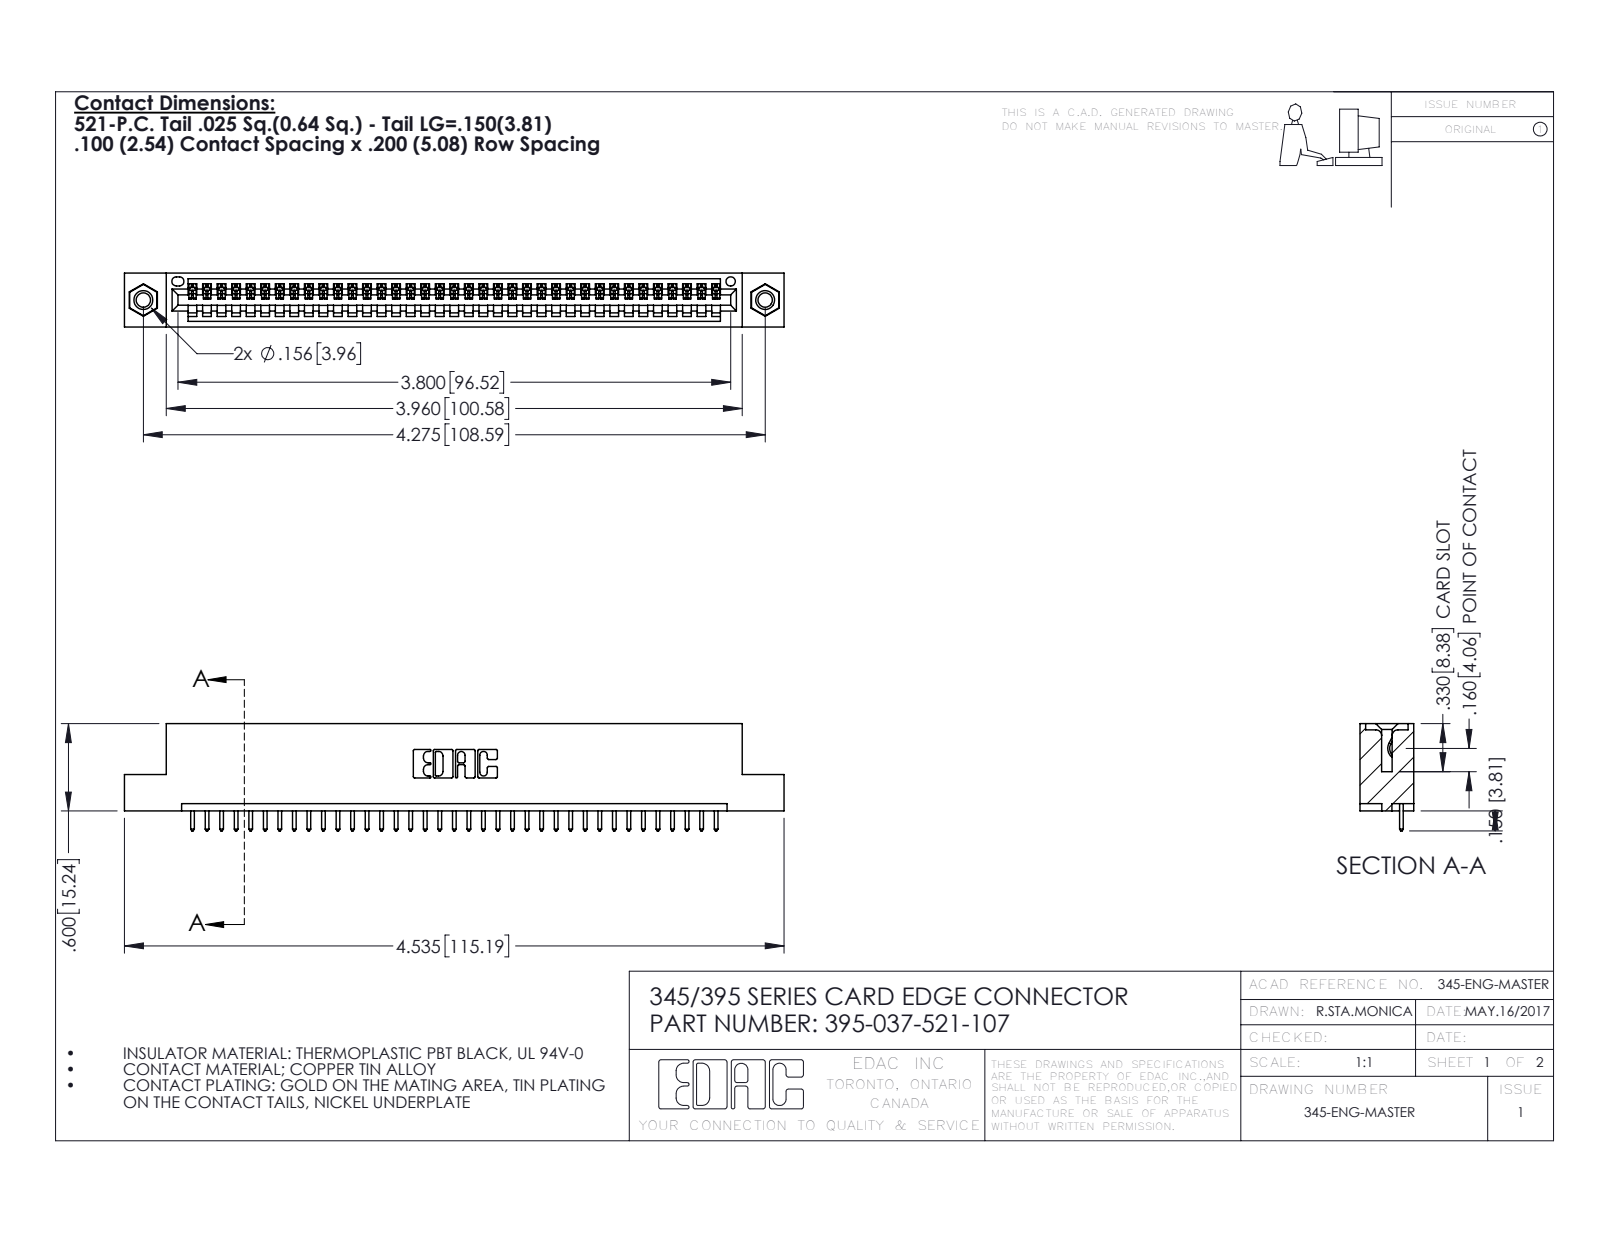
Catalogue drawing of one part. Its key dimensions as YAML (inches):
part_name: "345-250-001_345-250-005-103; 345-292-001_345-293-121; 345 Part_Flush Mounting Lugs - 0.156 Dia-TI; 395-037-521-107"
step_written_by: "SolidWorks 2016 (CONFIG_CONTROL_DESIGN)"
units: inches
bodies: {solids: 40, faces: 2332, planar: 1592, cylindrical: 724, other: 16}
overall_size: [4.535, 0.737, 0.37]
volume: 0.658
surface_area: 21.51
round_holes:
  - {diameter: 0.098, count: 2}
  - {diameter: 0.125, count: 2}
  - {diameter: 0.156, count: 2}
  - {diameter: 0.064, count: 1}
round_bosses_or_shafts:
  - {diameter: 0.155, count: 2}
partial_cylinders:
  - {radius: 0.006, count: 74}
  - {radius: 0.01, count: 74}
  - {radius: 0.01, count: 22}
  - {radius: 0.007, count: 6}
  - {radius: 0.031, count: 6}
  - {radius: 0.026, count: 3}
  - {radius: 0.031, count: 2}
  - {radius: 0.04, count: 2}
face_to_face_distances: [0.072, 0.298, 0.37, 0.2, 0.098, 0.272, 0.025, 0.225, 0.149, 0.072]
hole_center_spacings: [0.27, 4.039, 4.275]
